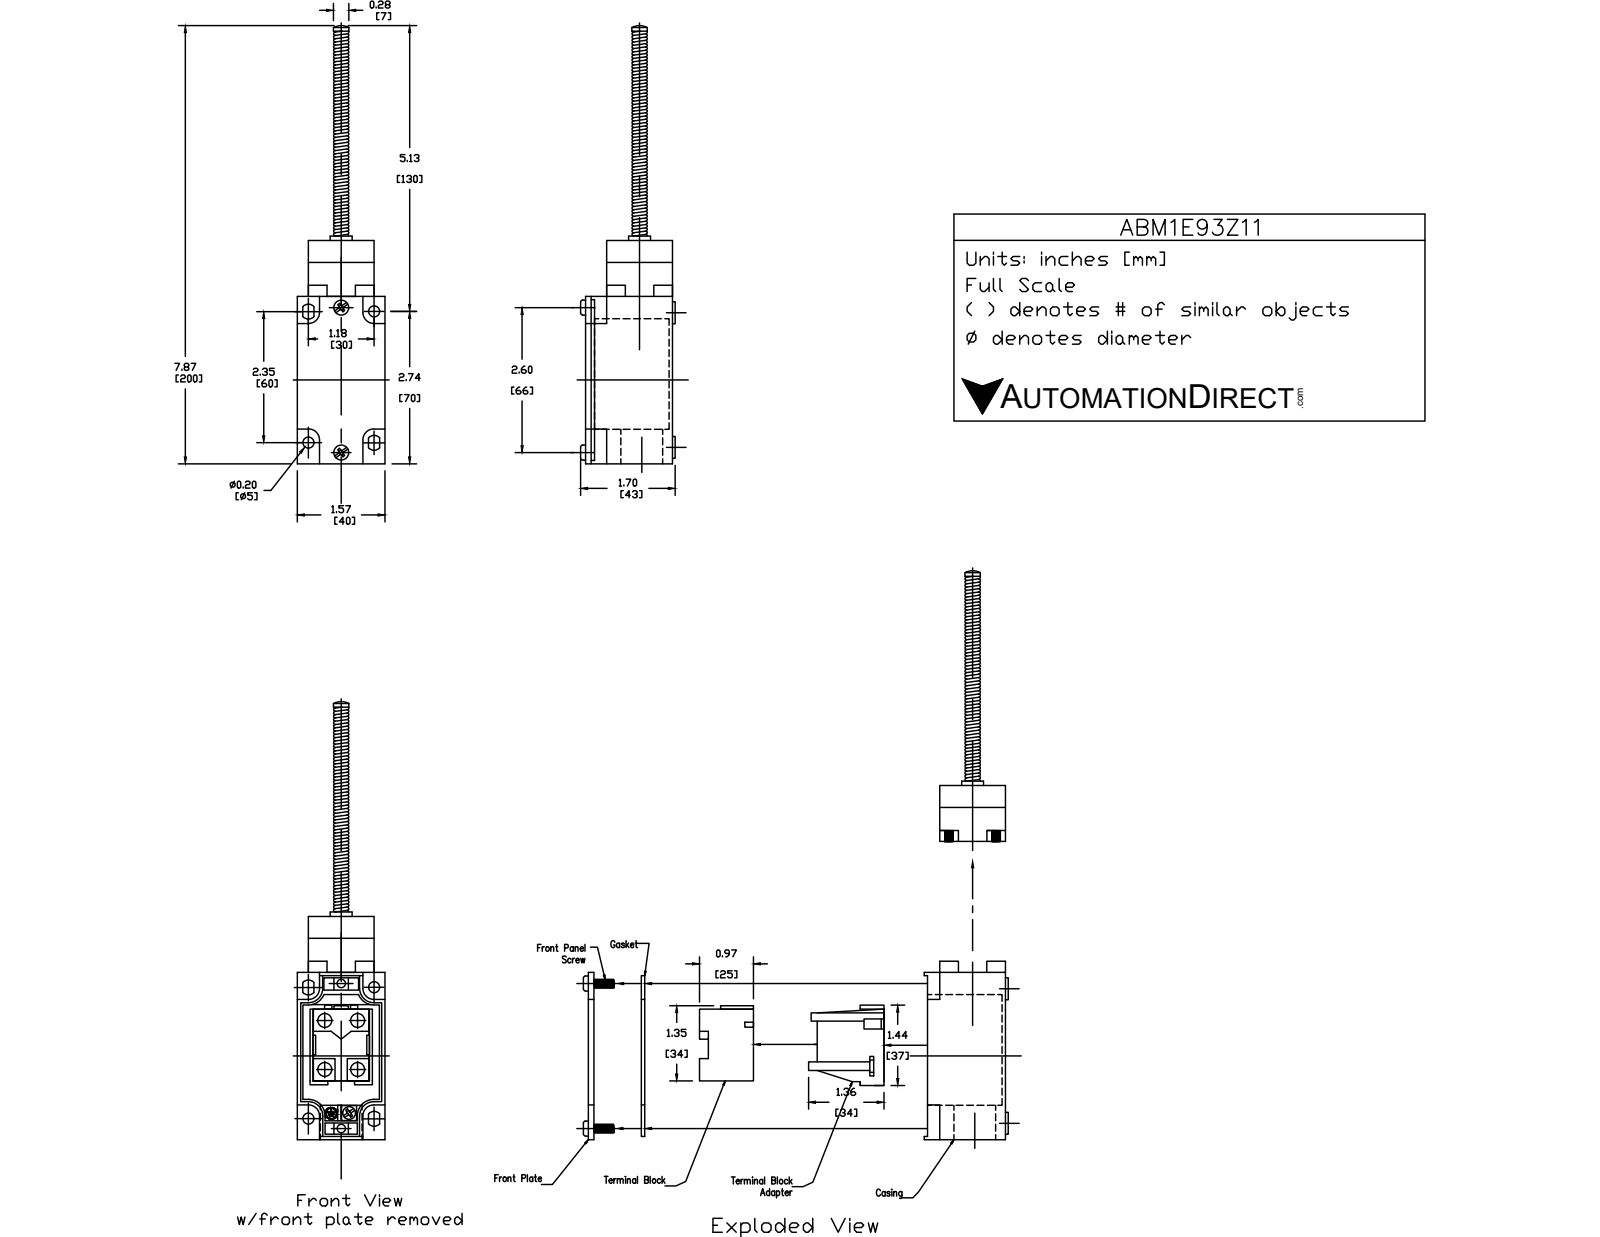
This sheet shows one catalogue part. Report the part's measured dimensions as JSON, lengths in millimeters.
{"part_name": "ABM1E93Z11", "step_written_by": "SolidWorks 2017 (AUTOMOTIVE_DESIGN)", "units": "millimeters", "bodies": {"solids": 3, "faces": 196, "planar": 78, "cylindrical": 84, "other": 34}, "overall_size": [198.3, 43.3, 40], "volume_mm3": 130500, "surface_area_mm2": 25350, "round_holes": [[5.2, 2], [17, 1], [19, 1], [20.5, 1]], "round_bosses_or_shafts": [[7, 7], [10, 4], [19, 1], [11.7, 1], [6.8, 1]], "partial_cylinders_radius": [[1.5, 16], [0.5, 4], [0.6, 4], [5, 4], [3.3, 2], [11.5, 1], [12, 1]], "face_to_face_distances": [40, 39.5, 30, 5, 76.5, 9.5, 35, 77, 0.5, 81.5], "hole_center_spacings": [1, 67.1]}
